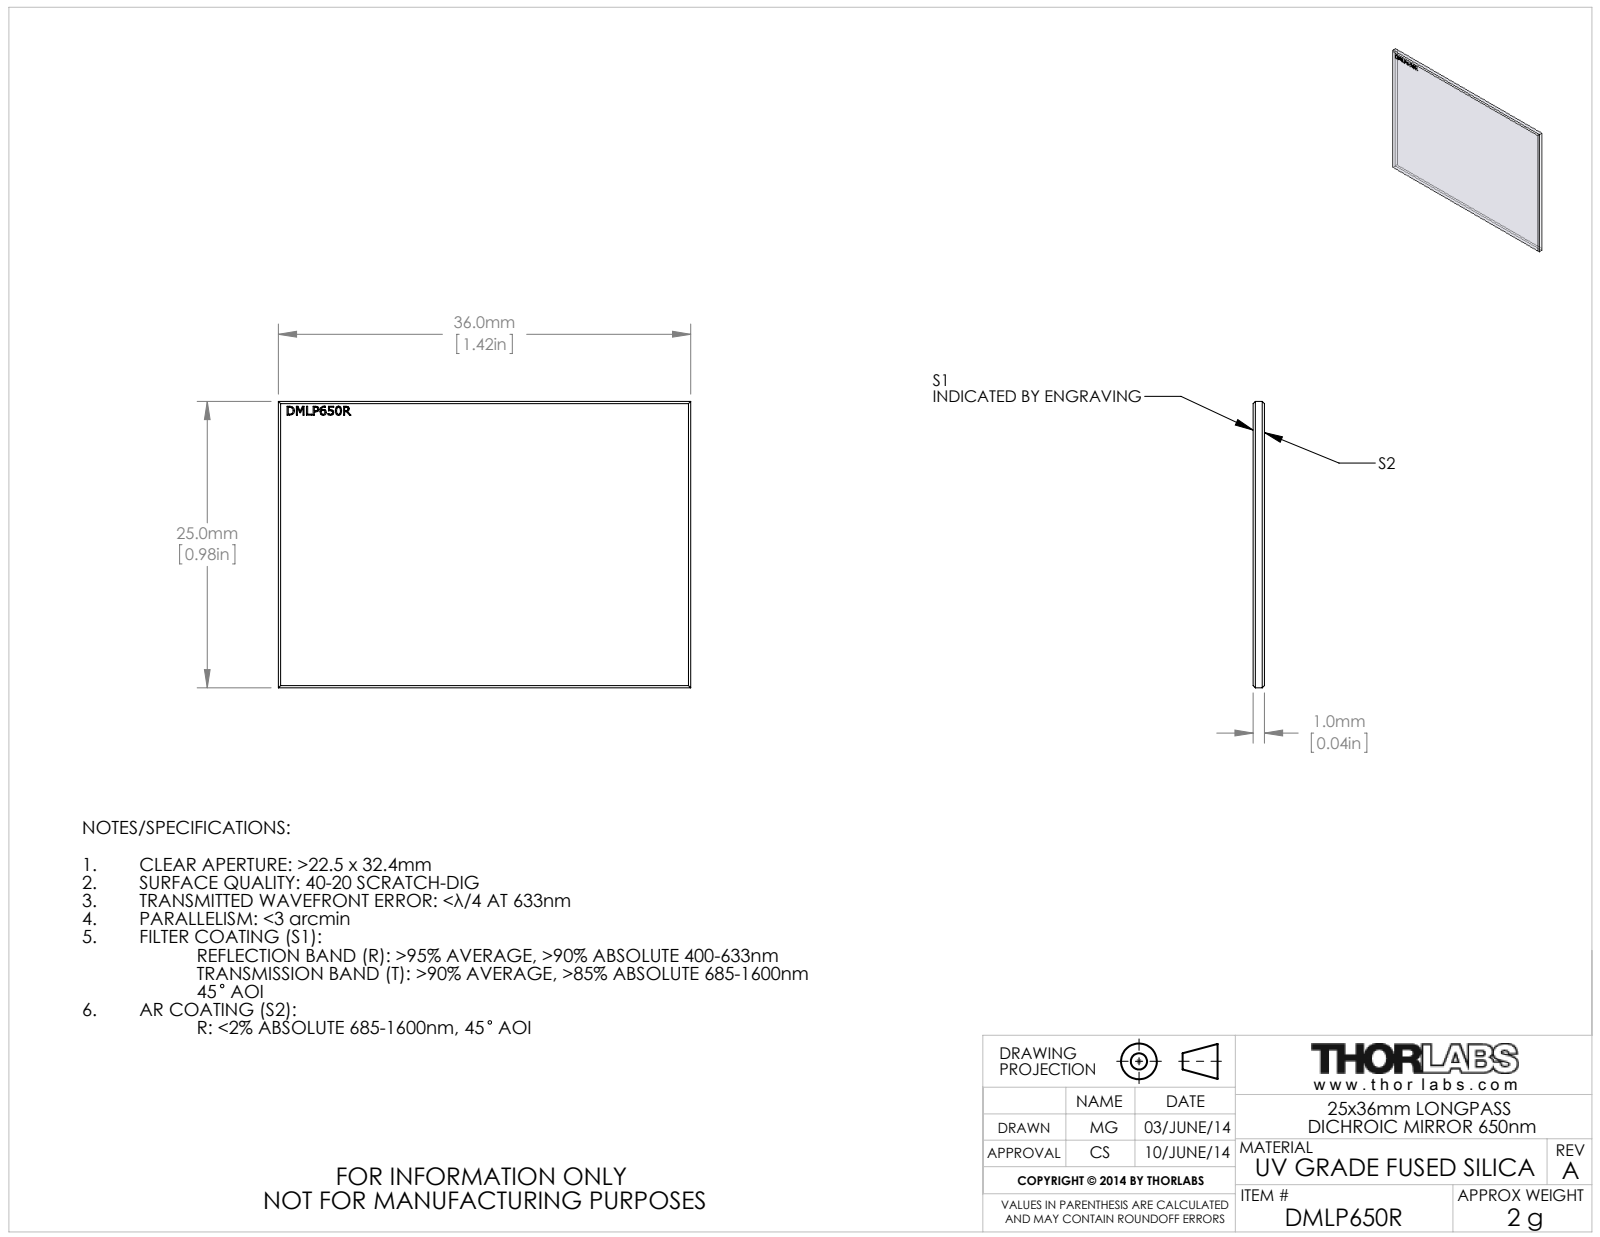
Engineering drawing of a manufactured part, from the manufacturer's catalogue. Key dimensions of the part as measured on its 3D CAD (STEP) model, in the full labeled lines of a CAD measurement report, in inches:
Part name (STEP PRODUCT): TTN028295-E0W
STEP written by: SolidWorks 2012 (CONFIG_CONTROL_DESIGN)
Units: inches
Bodies: 1 solid, 145 faces (80 planar, 0 cylindrical, 65 other)
Overall size (bounding box): 1.417 × 0.984 × 0.039
Volume: 0.055 in³ · Surface area: 2.934 in²
Main face-to-face distances: 0.039, 0.984, 0.713, 1.417, 1.019, 0.035, 0.023, 0.032, 0.967, 0.017
